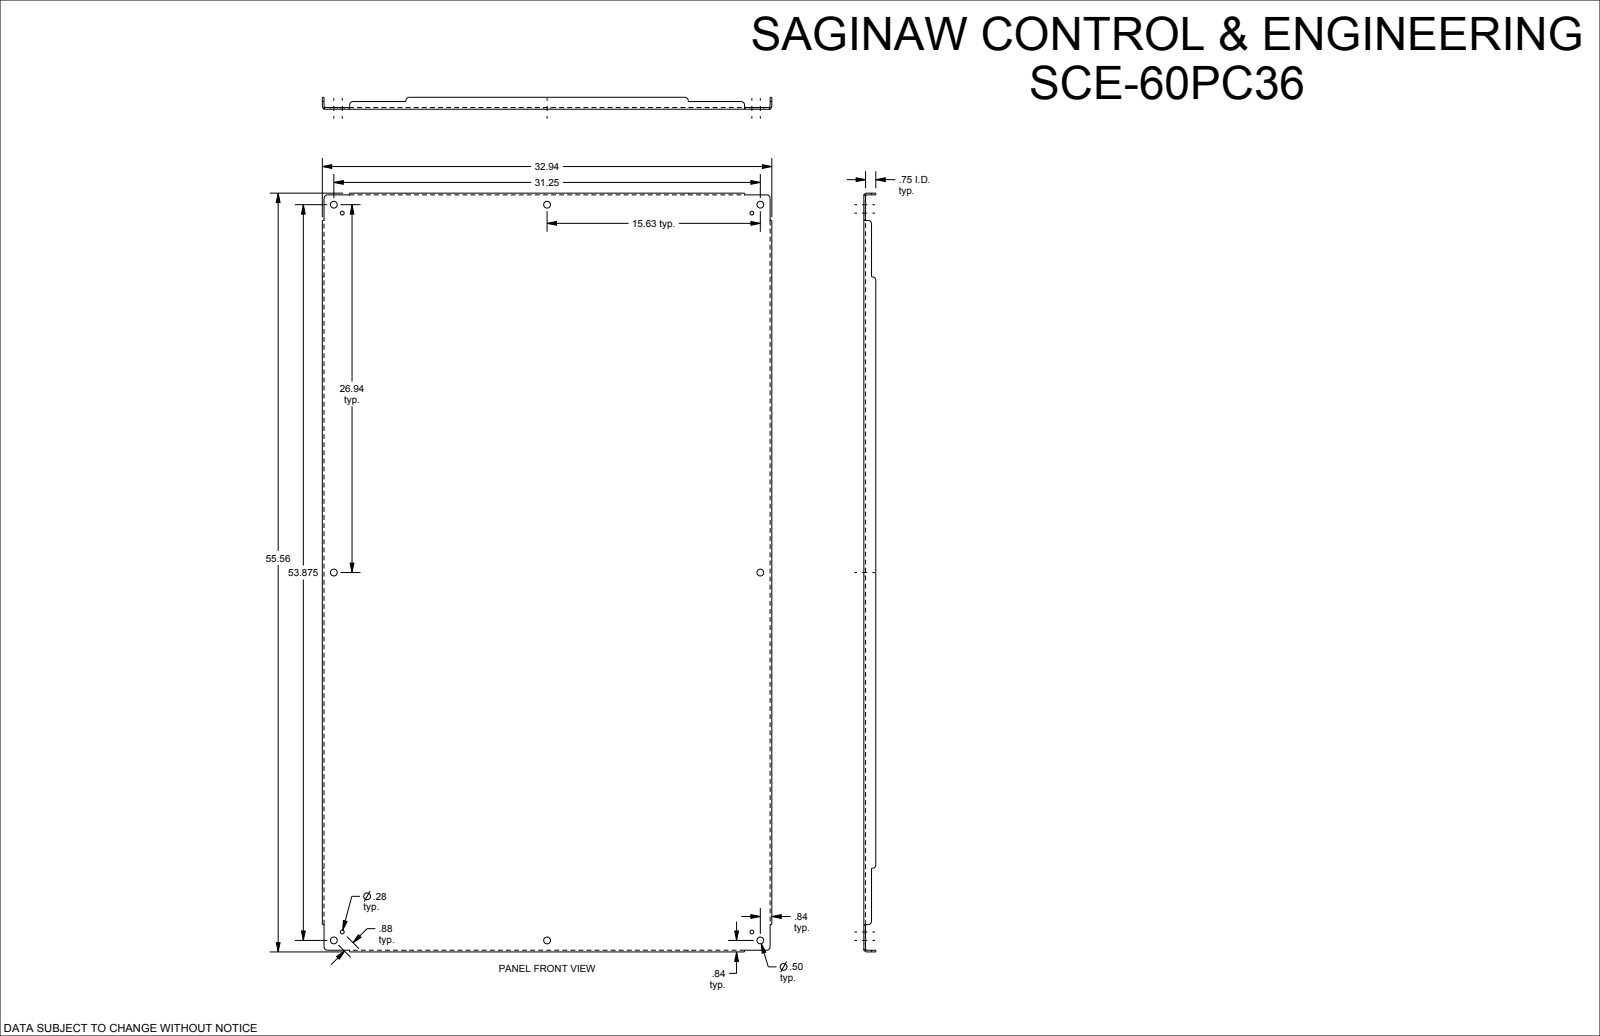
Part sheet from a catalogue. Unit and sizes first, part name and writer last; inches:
Units: inches
Overall size (bounding box): 55.563 × 32.938 × 0.875
Round holes (diameter × count): ⌀0.5 ×8, ⌀0.281 ×4
Partial cylindrical surfaces — rounded edges, fillets, slot ends (radius × count): R0.25 ×12, R0.112 ×4, R0.237 ×4
Main face-to-face distances: 0.125, 0.125, 32.813, 55.437, 32.687, 32.938, 55.313, 55.562, 0.75, 0.875
Hole centre spacings: 0.875, 15.019, 15.625, 26.326, 26.937, 30.638, 31.141, 40.385
Volume: 240.6 in³ · Surface area: 3 873 in²
Bodies: 1 solid, 110 faces (46 planar, 40 cylindrical, 24 other)
Part name (STEP PRODUCT): SCE-60PC36
STEP written by: SolidWorks 2019 (CONFIG_CONTROL_DESIGN)
